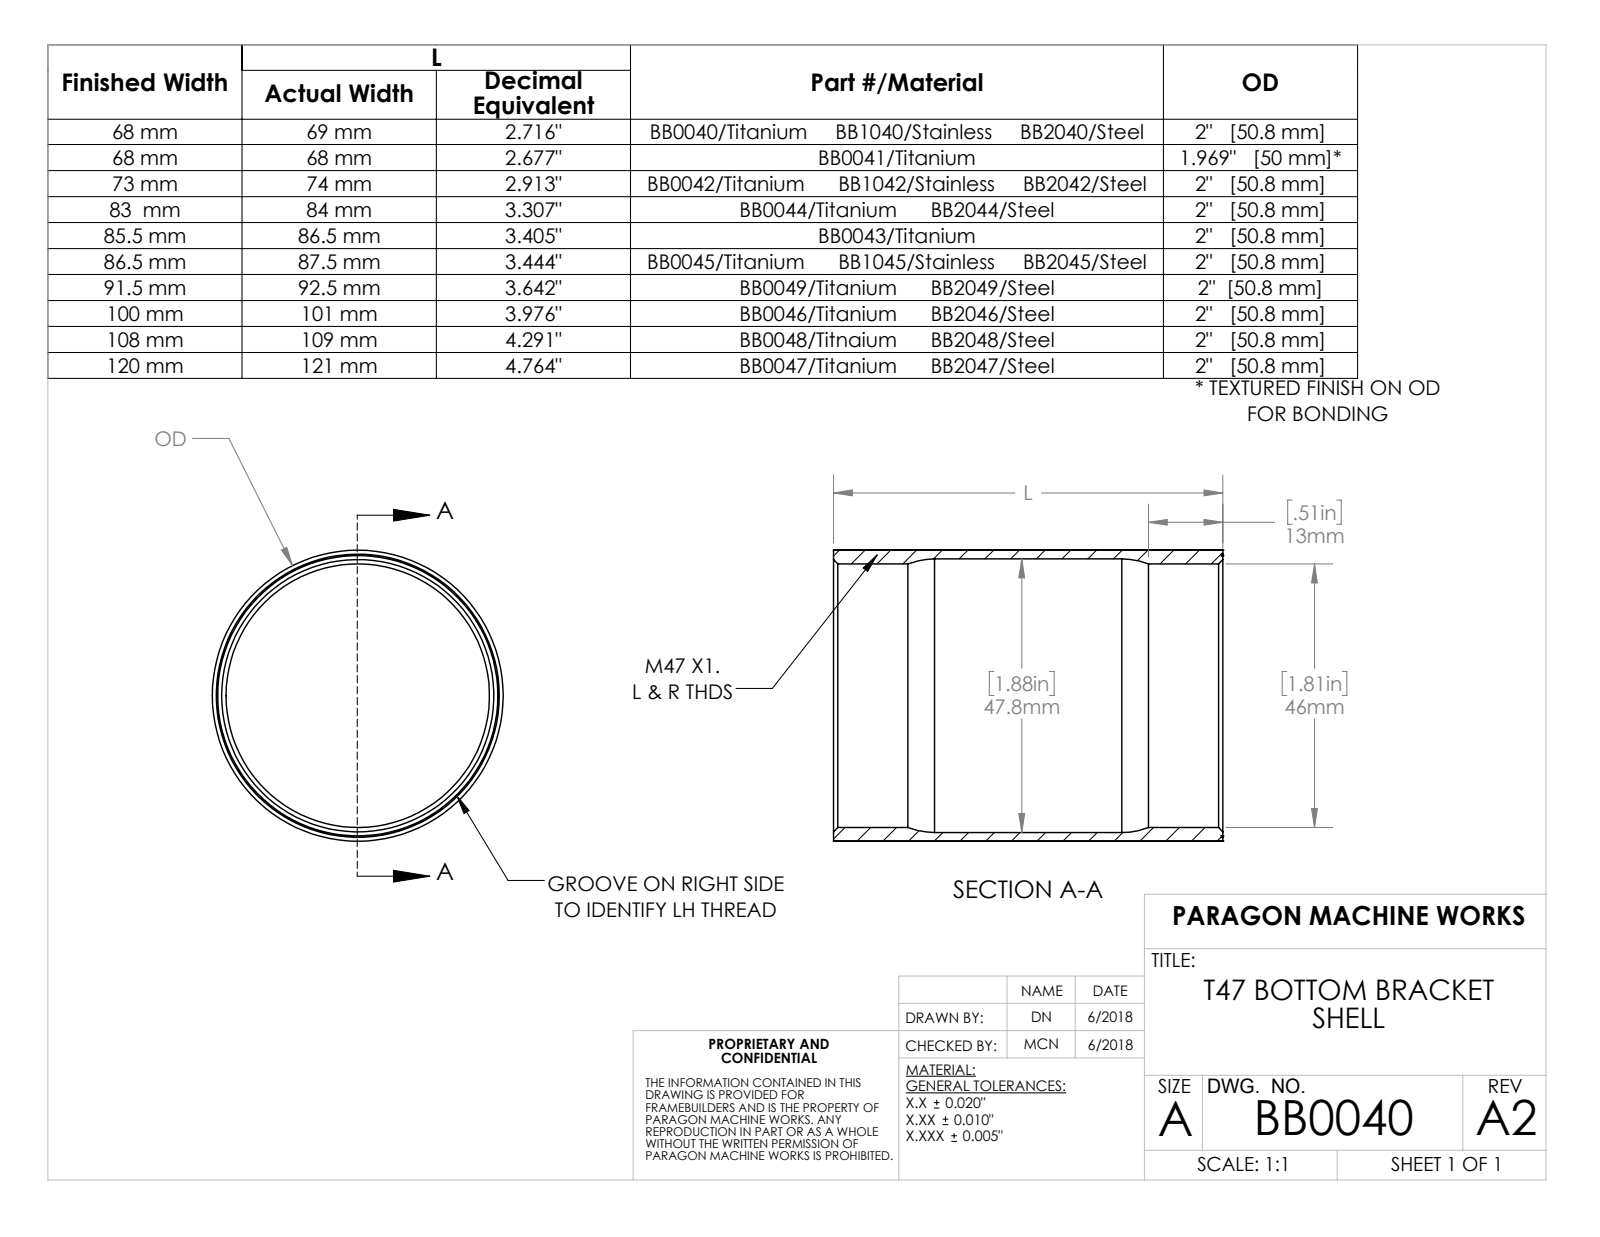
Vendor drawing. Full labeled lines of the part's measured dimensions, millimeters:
Part name (STEP PRODUCT): BB0040
STEP written by: SolidWorks 2015 (AUTOMOTIVE_DESIGN)
Units: millimetres
Bodies: 1 solid, 24 faces (4 planar, 12 cylindrical, 8 other)
Overall size (bounding box): 69 × 50.8 × 50.8
Volume: 22 140 mm³ · Surface area: 21 800 mm²
Round holes (diameter × count): ⌀46 ×1, ⌀47 ×1, ⌀49.4 ×1
Round bosses / shafts (diameter × count): ⌀50.8 ×1, ⌀48.9 ×1
Main face-to-face distances: 69, 68.7
